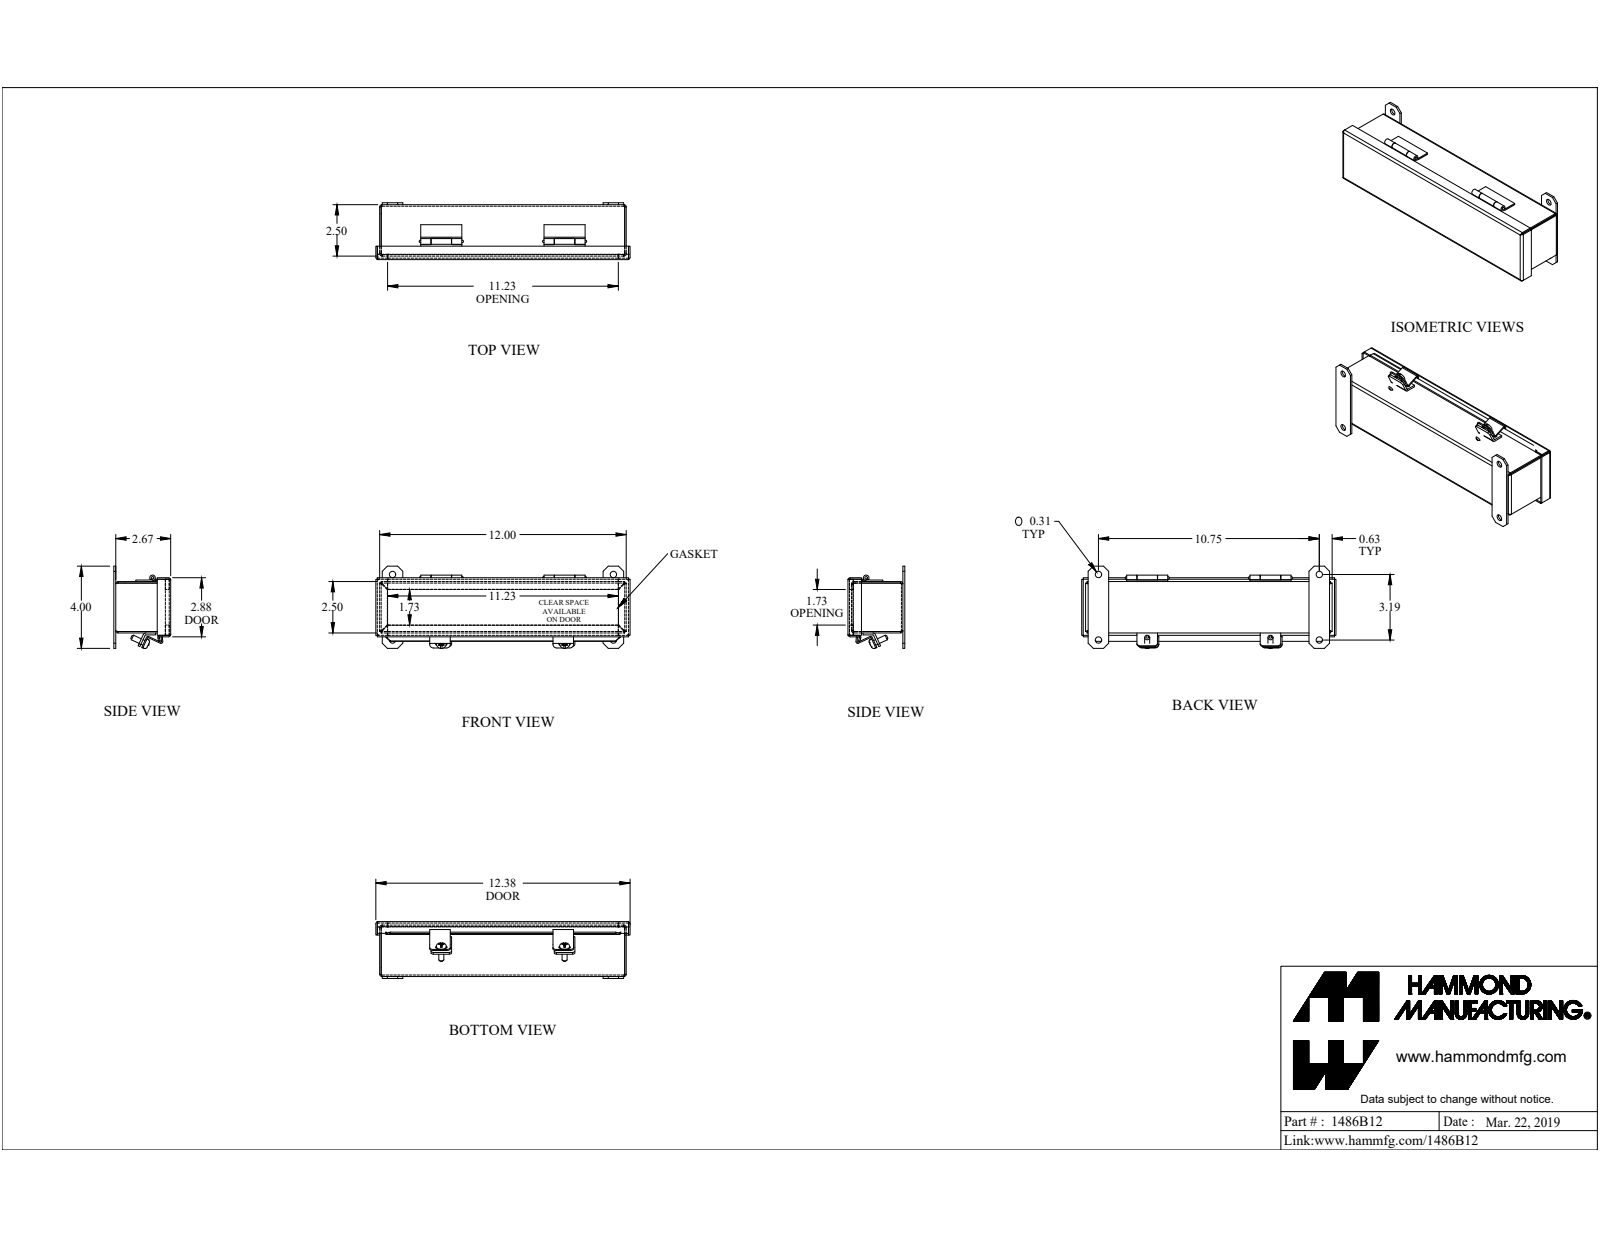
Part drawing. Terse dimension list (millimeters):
name: 1486B12
written by: SolidWorks 2019 (CONFIG_CONTROL_DESIGN)
unit: mm
bodies: 20 solids, 420 faces (278 planar, 98 cylindrical, 44 other)
size: 314.3 × 101.8 × 70.3
volume: 261 000 mm³; area: 267 600 mm²
holes: 4× ⌀8, 2× ⌀5.4, 1× ⌀3.2
bosses: 2× ⌀12.2, 2× ⌀6.2, 1× ⌀7, 1× ⌀3.2
rounds: 13× R0.9, 13× R2.7, 12× R6.4, 8× R4.8, 4× R0.3, 4× R3.6, 2× R0.7, 2× R2.2
face distances: 1.8, 61.7, 66, 63.5, 59.8, 67.9, 64.2, 4.7, 66.4, 4.7
hole spacings: 81, 284.8, 152.4, 273.1, 273.1
